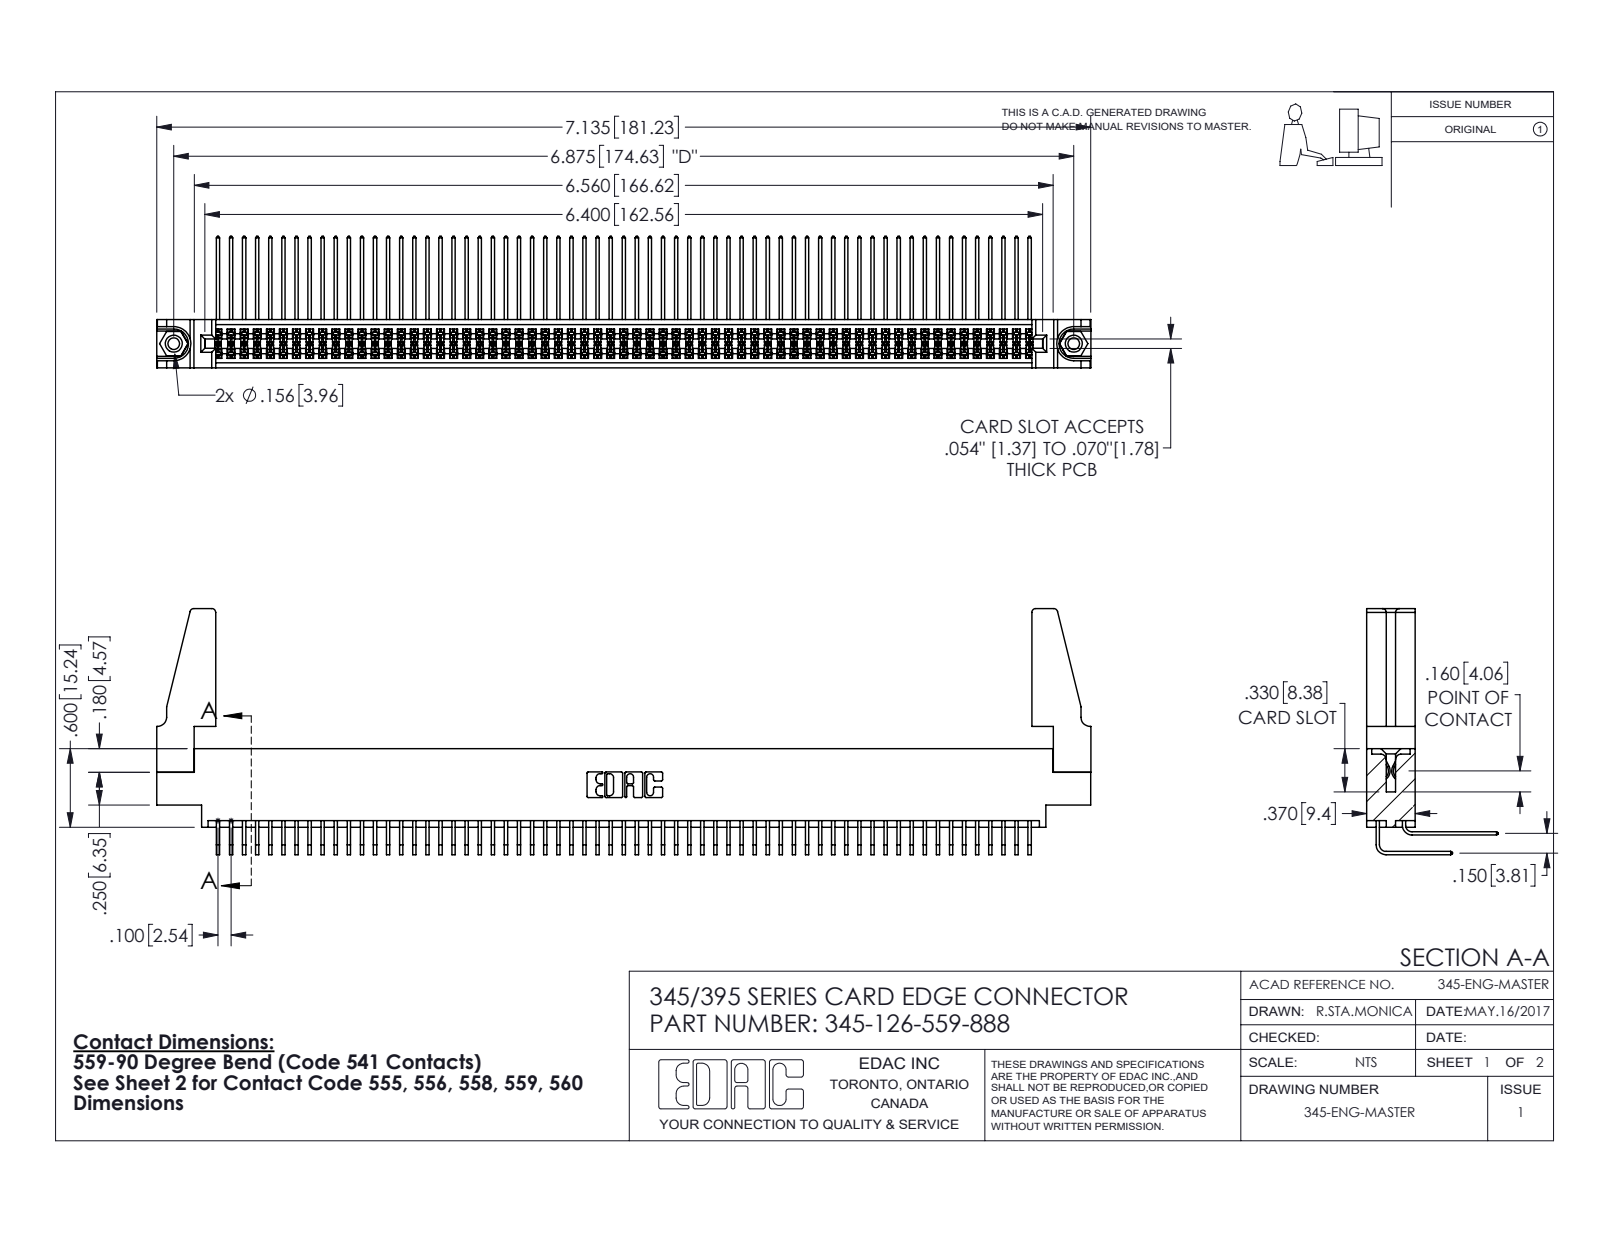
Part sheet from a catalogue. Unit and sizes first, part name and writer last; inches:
Units: inches
Overall size (bounding box): 7.136 × 1.879 × 1.005
Round holes (diameter × count): ⌀0.089 ×2, ⌀0.125 ×2, ⌀0.156 ×2, ⌀0.064 ×1
Round bosses / shafts (diameter × count): ⌀0.155 ×2
Partial cylindrical surfaces — rounded edges, fillets, slot ends (radius × count): R0.006 ×251, R0.01 ×22, R0.03 ×8, R0.007 ×6, R0.031 ×6, R0.026 ×3, R0.014 ×2, R0.019 ×2
Main face-to-face distances: 0.072, 0.298, 0.37, 0.2, 0.098, 0.272, 0.025, 0.225, 0.15, 0.175
Hole centre spacings: 0.27, 6.639, 6.875
Volume: 1.322 in³ · Surface area: 53.18 in²
Bodies: 131 solids, 6806 faces (4566 planar, 2224 cylindrical, 16 other)
Part name (STEP PRODUCT): 345-126-559-888; 345-292-001_559 Tail - 2; 345-250-001_345-250-001-102; 345 Part_0.170 Offset - 0.156 Dia-TH (+2 more)
STEP written by: SolidWorks 2016 (CONFIG_CONTROL_DESIGN)
